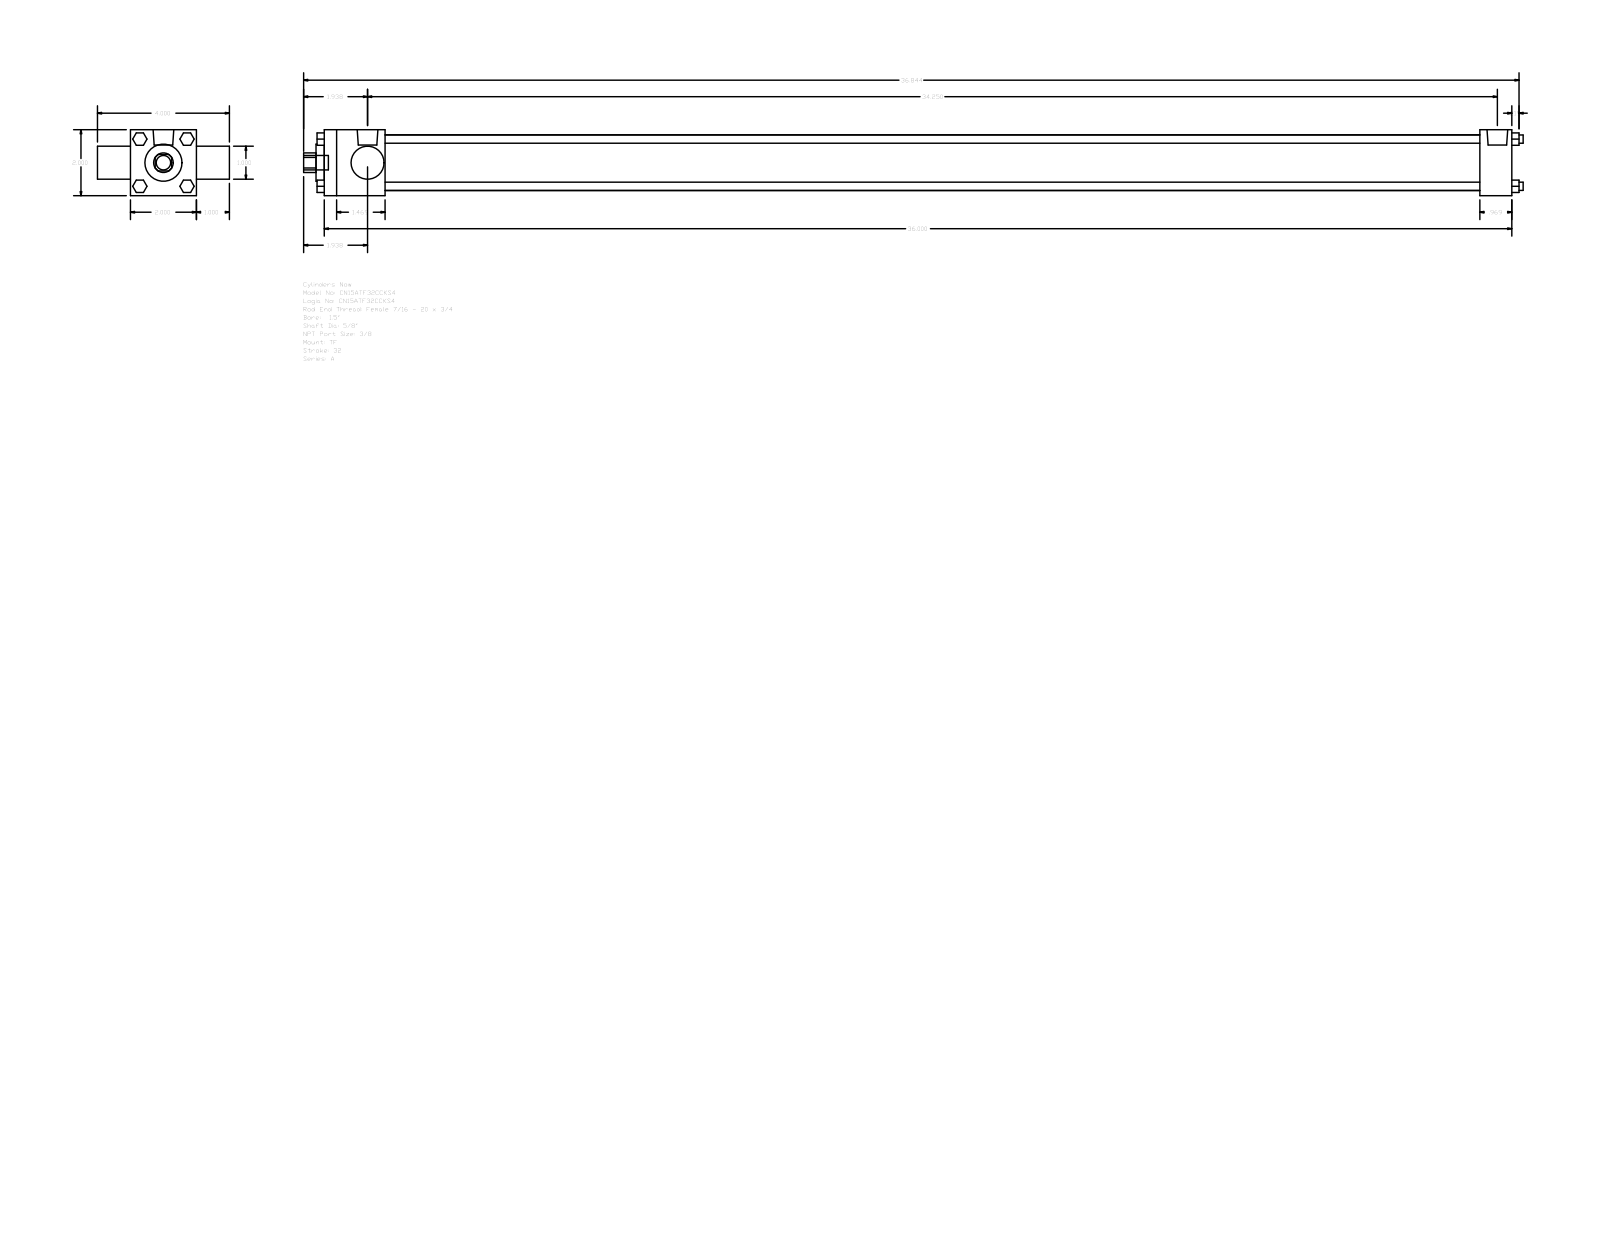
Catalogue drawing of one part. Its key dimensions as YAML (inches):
part_name: "A_TF__0150_0.625"
step_written_by: "GSSL Pune (CONFIG_CONTROL_DESIGN)"
units: inches
bodies: {solids: 0, faces: 120, planar: 92, cylindrical: 28, other: 0}
overall_size: [36.969, 4, 2]
round_holes:
  - {diameter: 0.625, count: 1}
  - {diameter: 1, count: 1}
  - {diameter: 1.125, count: 1}
  - {diameter: 1.69, count: 1}
round_bosses_or_shafts:
  - {diameter: 0.25, count: 4}
  - {diameter: 0.219, count: 3}
  - {diameter: 0.627, count: 2}
  - {diameter: 0.437, count: 1}
partial_cylinders:
  - {radius: 0.297, count: 1}
face_to_face_distances: [2, 36, 1, 3, 1.844, 35.031, 33.187, 34.156, 0.969, 0.375]
